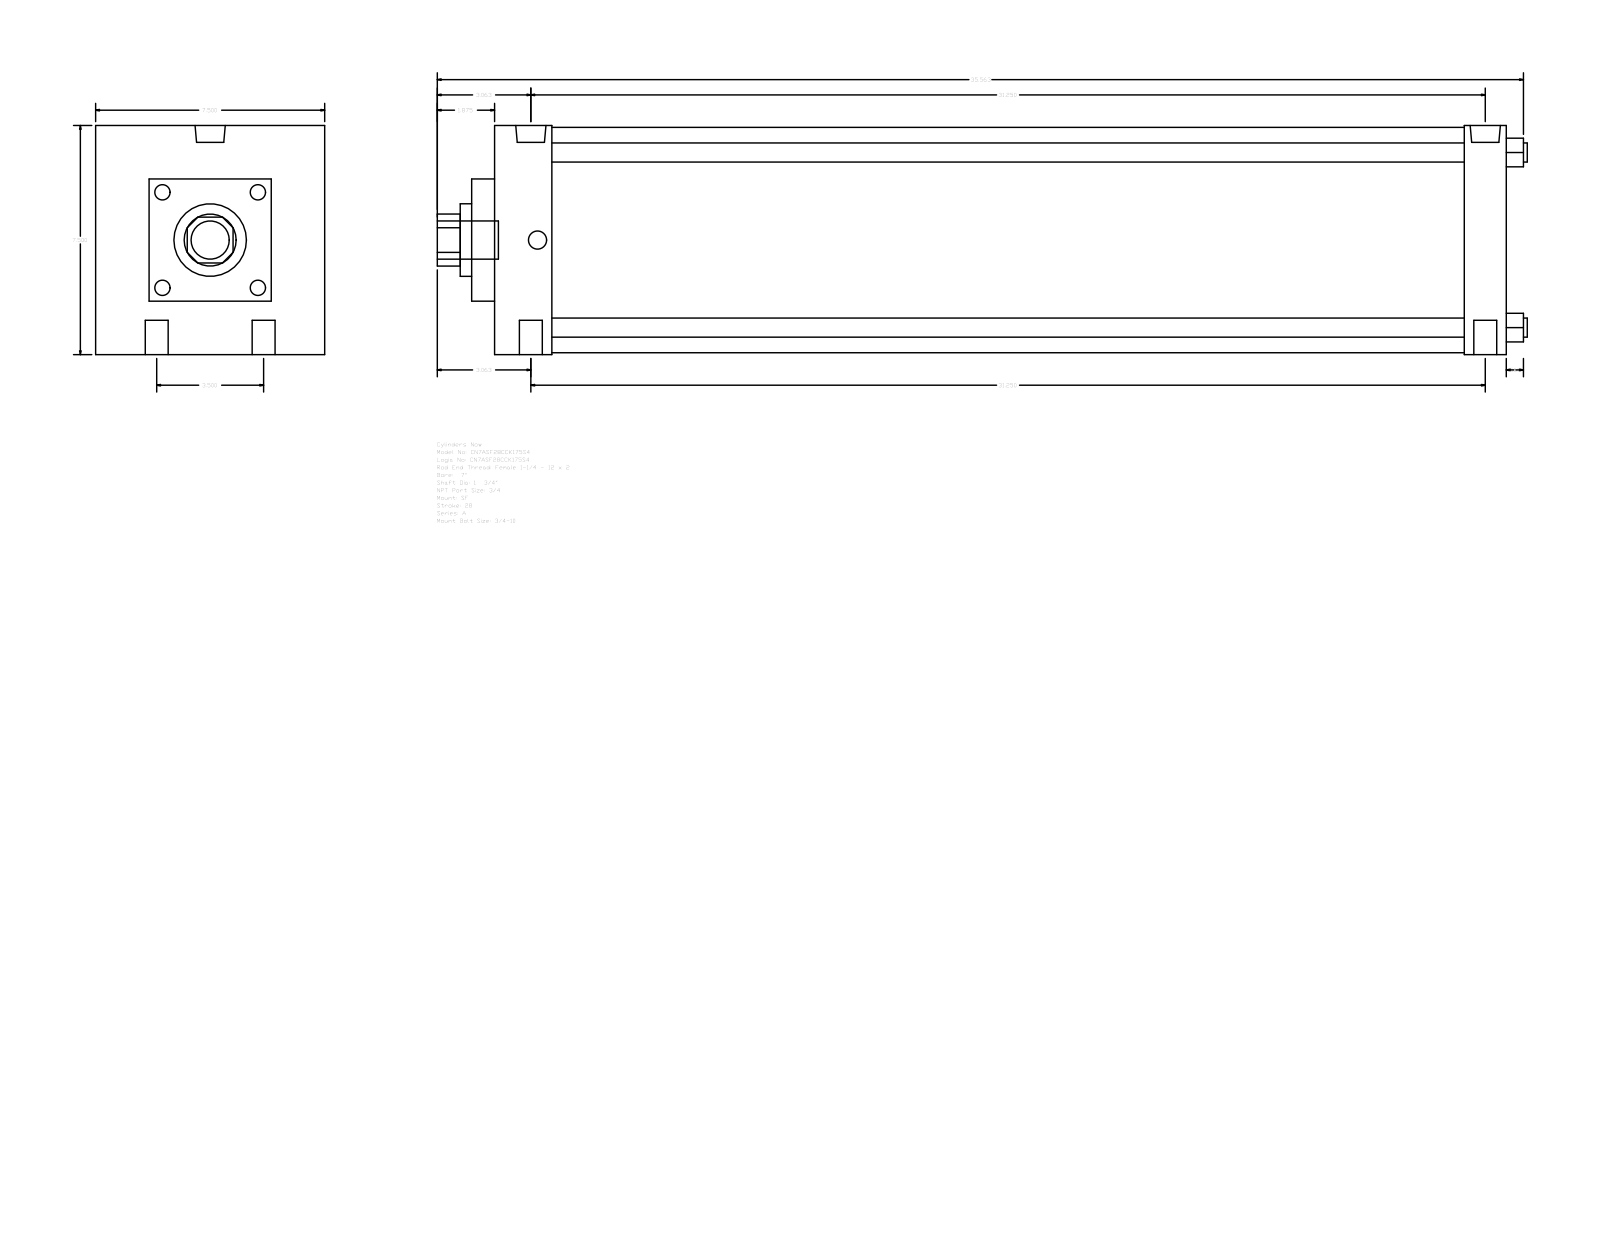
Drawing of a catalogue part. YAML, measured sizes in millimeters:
part_name: "A_SF__0700_1.75"
step_written_by: "GSSL Pune (CONFIG_CONTROL_DESIGN)"
units: millimeters
bodies: {solids: 0, faces: 93, planar: 67, cylindrical: 26, other: 0}
overall_size: [906.46, 190.5, 190.5]
round_holes:
  - {diameter: 19.05, count: 4}
  - {diameter: 15.08, count: 2}
  - {diameter: 25.12, count: 2}
  - {diameter: 44.45, count: 1}
  - {diameter: 60.33, count: 1}
round_bosses_or_shafts:
  - {diameter: 15.88, count: 4}
  - {diameter: 187.32, count: 1}
  - {diameter: 31.75, count: 1}
partial_cylinders:
  - {radius: 21.63, count: 1}
face_to_face_distances: [190.5, 841.38, 44.45, 34.92, 19.05, 47.63, 806.46, 758.83, 793.75, 146.05]
hole_center_spacings: [44.45, 794.99, 793.75, 88.9, 798.71, 782.63]
